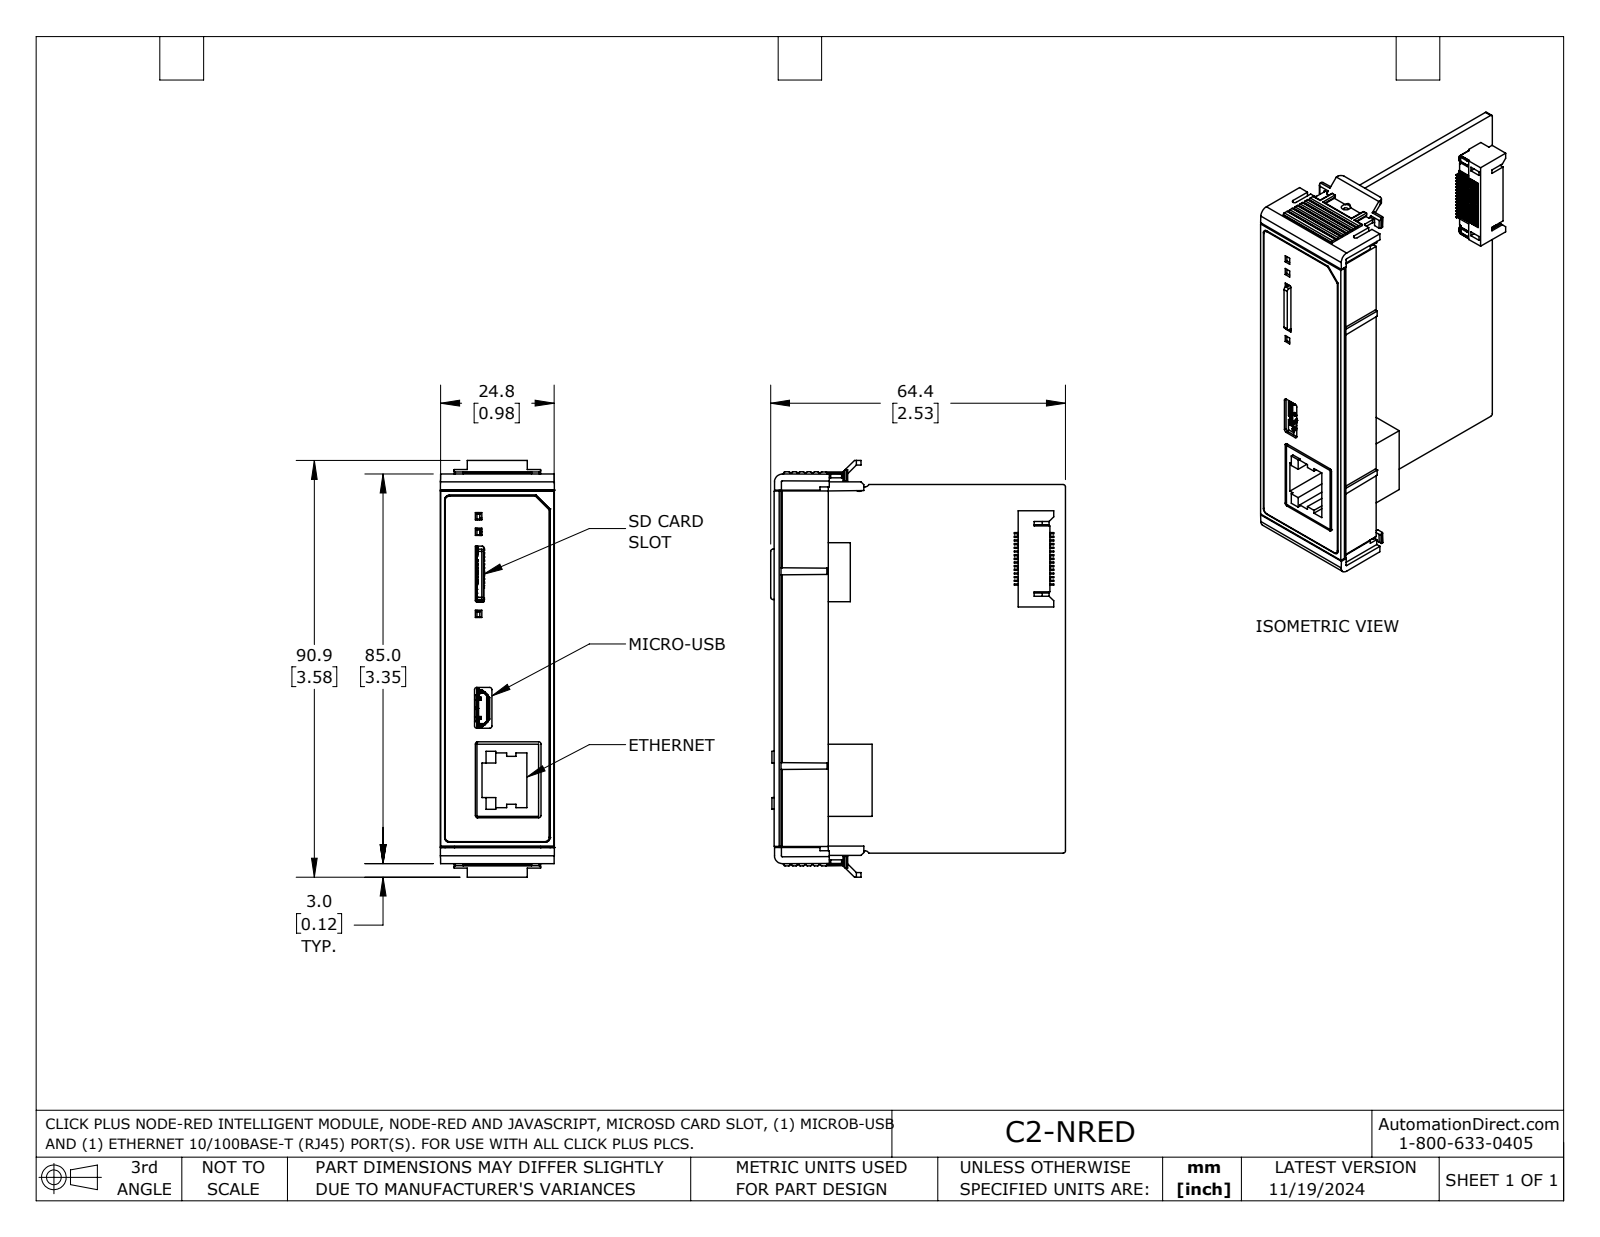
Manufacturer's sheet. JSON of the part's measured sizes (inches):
{"part_name": "C2-NRED", "step_written_by": "SolidWorks 2023 (AUTOMOTIVE_DESIGN)", "units": "inches", "bodies": {"solids": 2, "faces": 2111, "planar": 1794, "cylindrical": 288, "other": 29}, "overall_size": [3.579, 2.533, 0.98], "volume_in3": 1.147, "surface_area_in2": 41.98, "round_bosses_or_shafts": [[0.031, 12], [0.128, 2], [0.059, 2], [0.018, 1], [0.018, 1]], "partial_cylinders_radius": [[0.012, 79], [0.004, 32], [0.02, 26], [0.039, 17], [0.024, 15], [0.008, 14], [0.006, 12], [0.01, 10]], "face_to_face_distances": [0.063, 0.02, 0.851, 0.846, 0.067, 0.039, 0.047, 0.593, 0.53, 0.042]}
